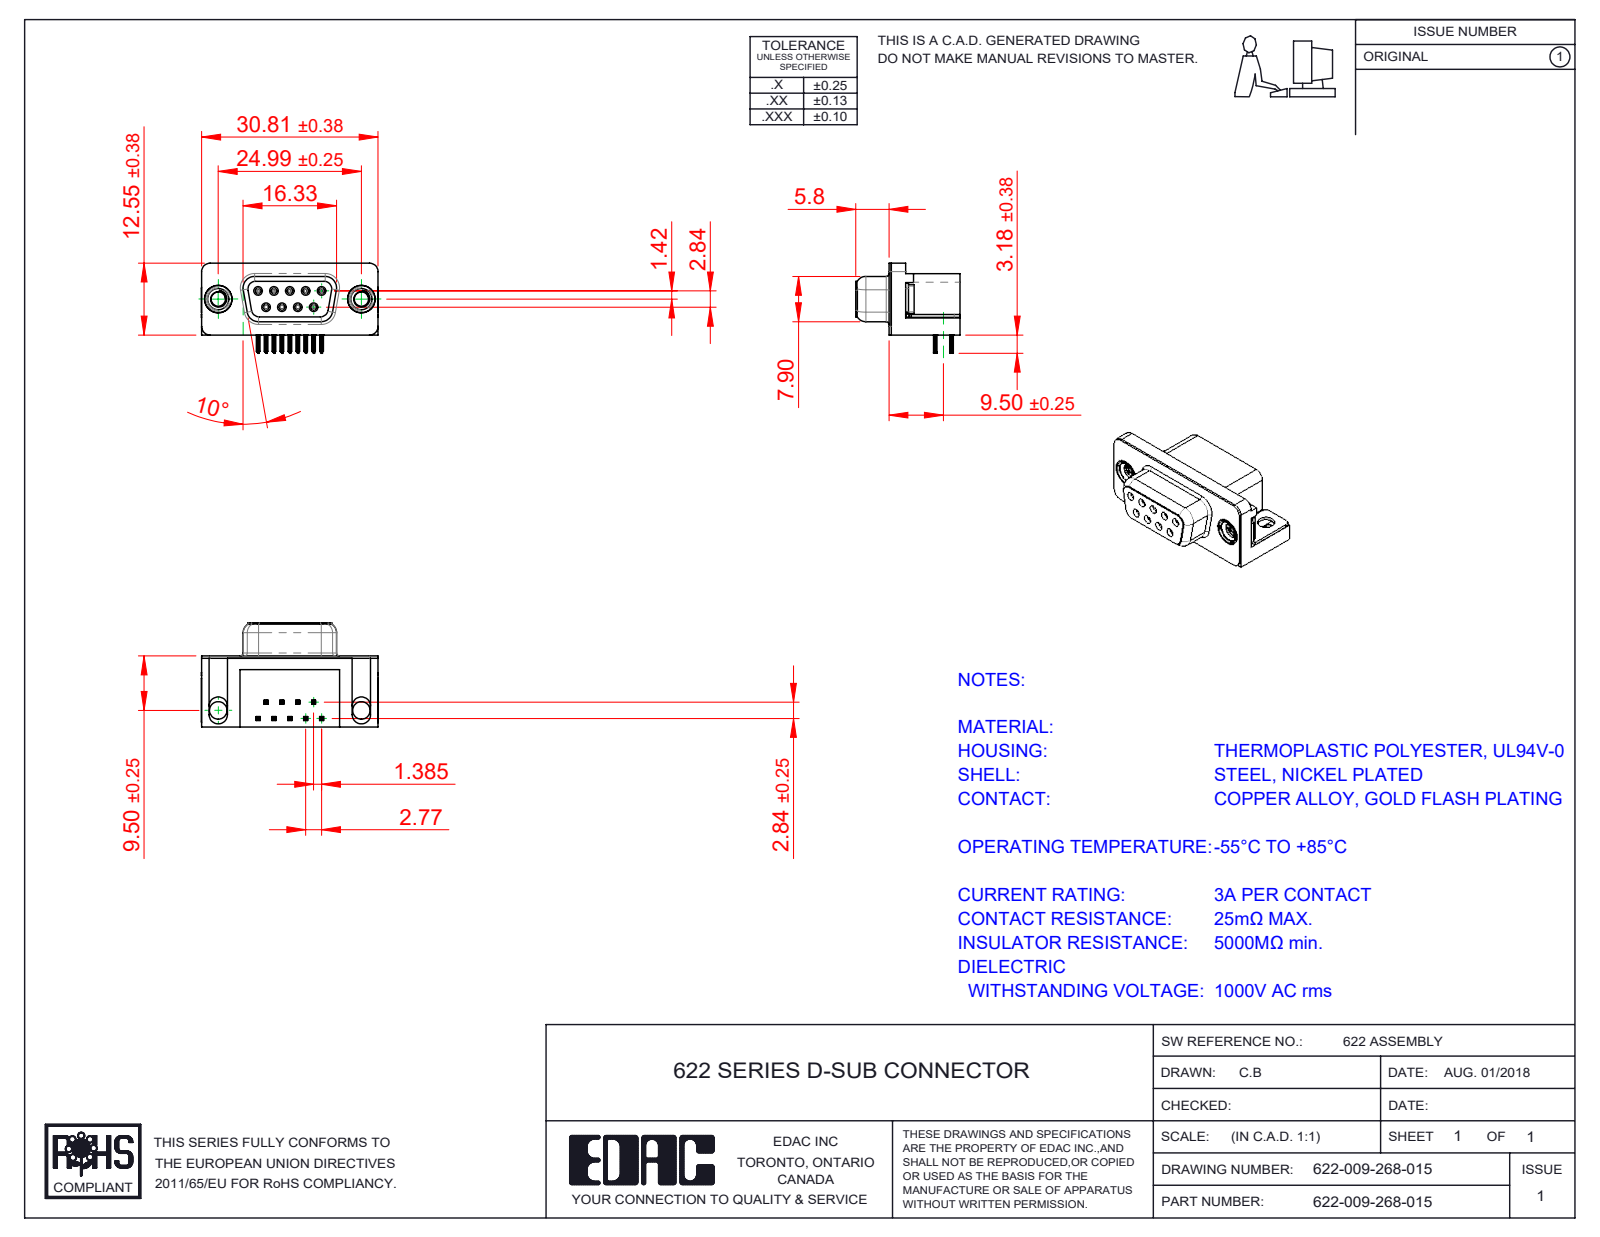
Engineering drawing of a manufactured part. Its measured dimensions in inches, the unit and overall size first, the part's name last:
Units: inches
Overall size (bounding box): 1.216 × 0.717 × 0.619
Round holes (diameter × count): ⌀0.031 ×9, ⌀0.035 ×9, ⌀0.098 ×2, ⌀0.12 ×2, ⌀0.157 ×2, ⌀0.189 ×2, ⌀0.197 ×2
Round bosses / shafts (diameter × count): ⌀0.047 ×9, ⌀0.193 ×2, ⌀0.187 ×2, ⌀0.154 ×2
Partial cylindrical surfaces — rounded edges, fillets, slot ends (radius × count): R0.004 ×72, R0.006 ×36, R0.014 ×18, R0.039 ×18, R0.013 ×9, R0.01 ×8, R0.053 ×8, R0.063 ×8
Main face-to-face distances: 0.016, 0.472, 0.488, 0.014, 0.114, 0.098, 0.244, 0.407, 0.02, 0.374
Hole centre spacings: 0.124, 0.109, 0.218, 0.198, 0.198, 0.327, 0.294, 0.295
Volume: 0.227 in³ · Surface area: 7.849 in²
Bodies: 15 solids, 1570 faces (682 planar, 420 cylindrical, 468 other)
Part name (STEP PRODUCT): 622 Housing_9 Socket; 622-009-268-015; 622 Socket Bottom; 622 Shell_9 Socket (+3 more)
STEP written by: SolidWorks 2016 (CONFIG_CONTROL_DESIGN)
